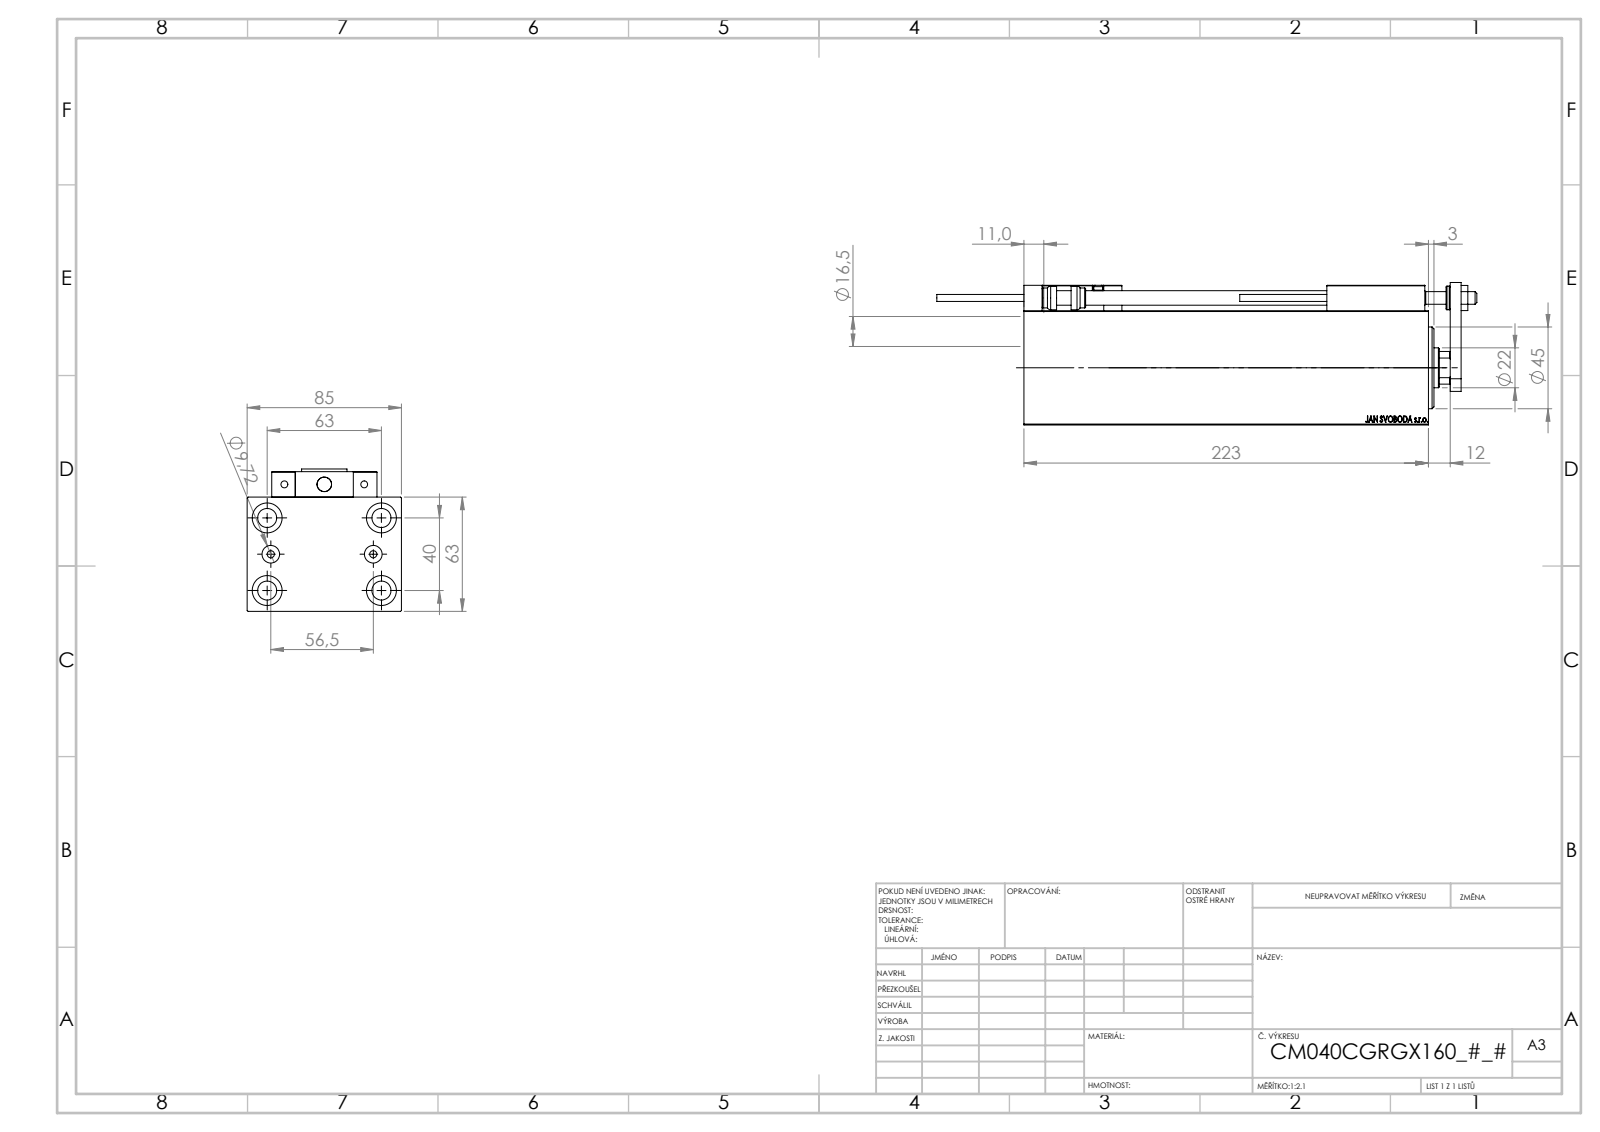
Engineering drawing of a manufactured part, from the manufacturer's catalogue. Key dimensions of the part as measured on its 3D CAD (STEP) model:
Part name (STEP PRODUCT): MAGNET; V450CM_C_Body; Block; SWITCH DIM B,W (+7 more)
STEP written by: SolidWorks 2019 (CONFIG_CONTROL_DESIGN)
Units: millimetres
Bodies: 23 solids, 1278 faces (560 planar, 184 cylindrical, 534 other)
Overall size (bounding box): 297.7 × 85 × 78.5
Volume: 1 019 000 mm³ · Surface area: 193 721 mm²
Round holes (diameter × count): ⌀4 ×6, ⌀8 ×5, ⌀16.5 ×5, ⌀3.2 ×4, ⌀10.5 ×4, ⌀5 ×2, ⌀9.72 ×2, ⌀7 ×1, ⌀12.5 ×1, ⌀22 ×1, ⌀25.5 ×1, ⌀40 ×1
Round bosses / shafts (diameter × count): ⌀5 ×2, ⌀3.8 ×2, ⌀13 ×1, ⌀11 ×1
Partial cylindrical surfaces — rounded edges, fillets, slot ends (radius × count): R0.3 ×30, R3 ×2, R10.5 ×1
Main face-to-face distances: 63, 85, 12, 211, 223, 14, 77, 15, 18, 30
Hole centre spacings: 37.31, 11.37, 20, 20.1, 20.5, 29.59, 29.69, 36.06
